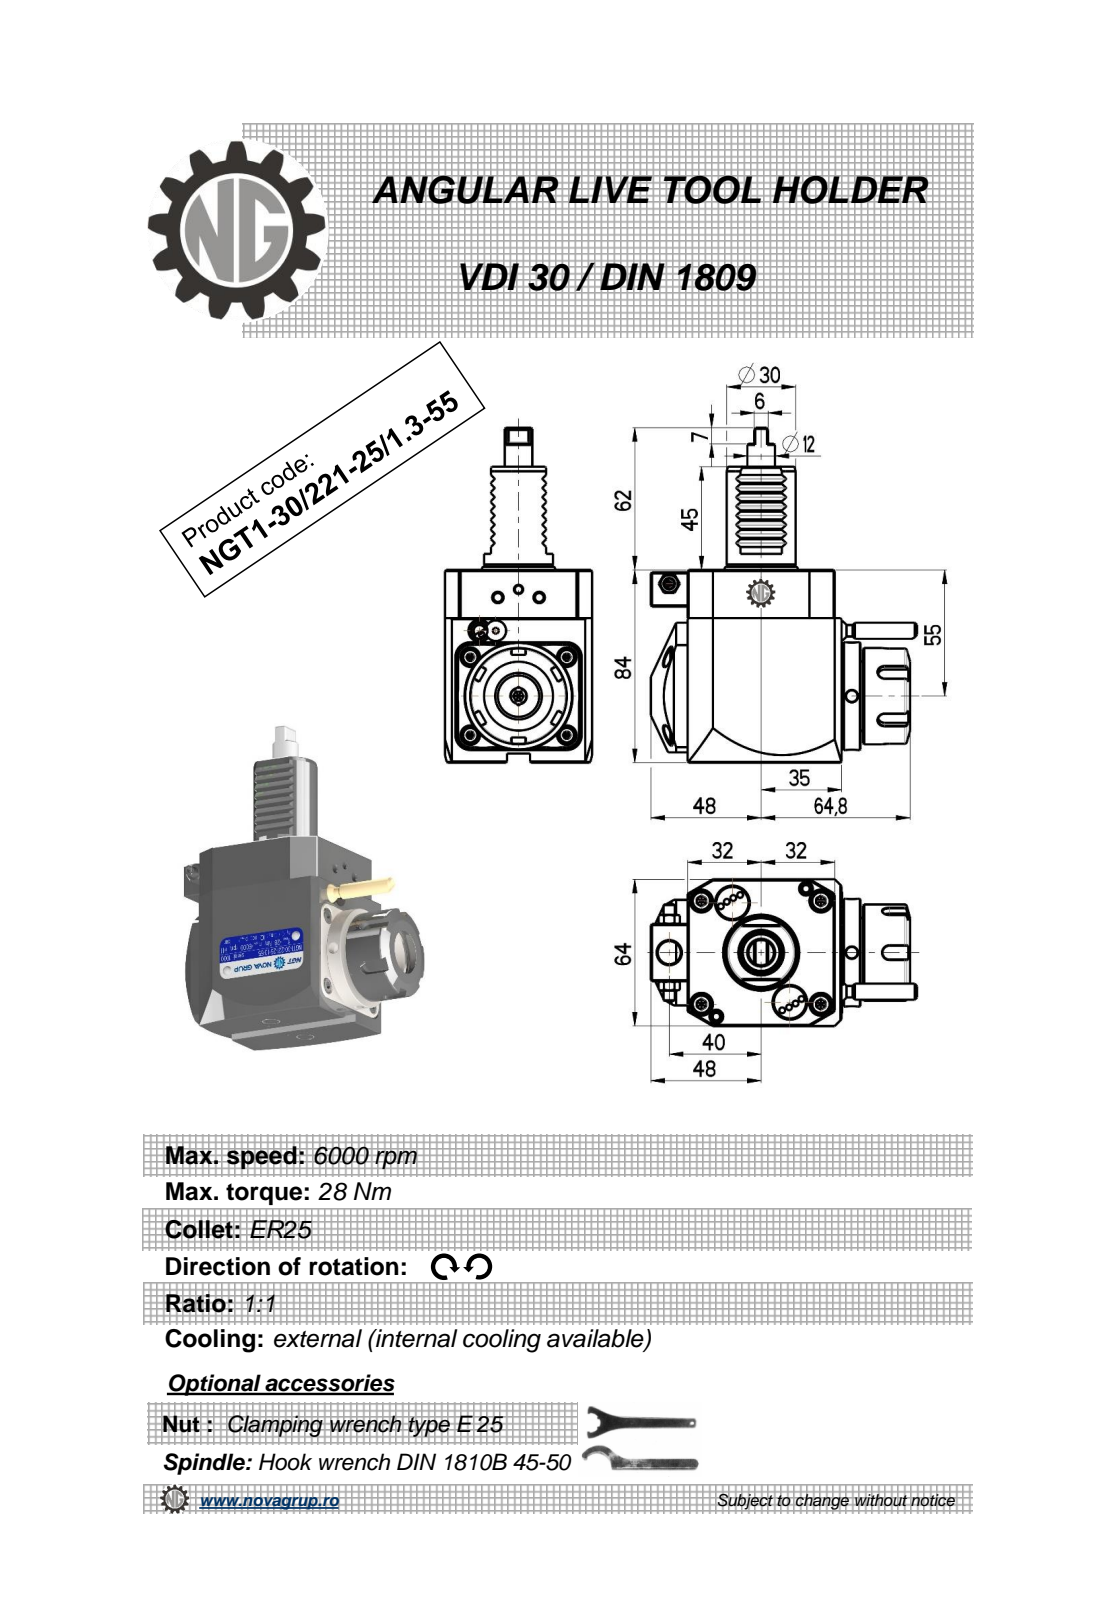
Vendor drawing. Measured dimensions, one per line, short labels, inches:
name: NGT1_30_221_25_1_3_55
written by: PRO/ENGINEER BY PARAMETRIC TECHNOLOGY CORPORATION, 2010280 (CONFIG_CONTROL_DESIGN)
unit: in
bodies: 1 solid, 470 faces (224 planar, 92 cylindrical, 154 other)
size: 5.748 × 4.56 × 2.52
volume: 27.22 in³; area: 71.55 in²
holes: 2× ⌀0.197, 1× ⌀0.098, 1× ⌀0.118, 1× ⌀0.165, 1× ⌀0.374, 1× ⌀0.394, 1× ⌀0.799
bosses: 2× ⌀0.353, 2× ⌀0.197, 1× ⌀1.85, 1× ⌀1.654, 1× ⌀1.378, 1× ⌀1.181, 1× ⌀0.472, 1× ⌀0.276
rounds: 16× R0.012, 12× R0.01, 5× R0.118, 4× R0.138, 2× R0.031, 2× R6.299, 1× R1.26
face distances: 2.52, 3.307, 0.02, 2.646, 3.15, 2.638, 3.268, 0.295, 0.118, 0.126
hole spacings: 0.975, 1.307, 1.831, 3.128, 3.675
